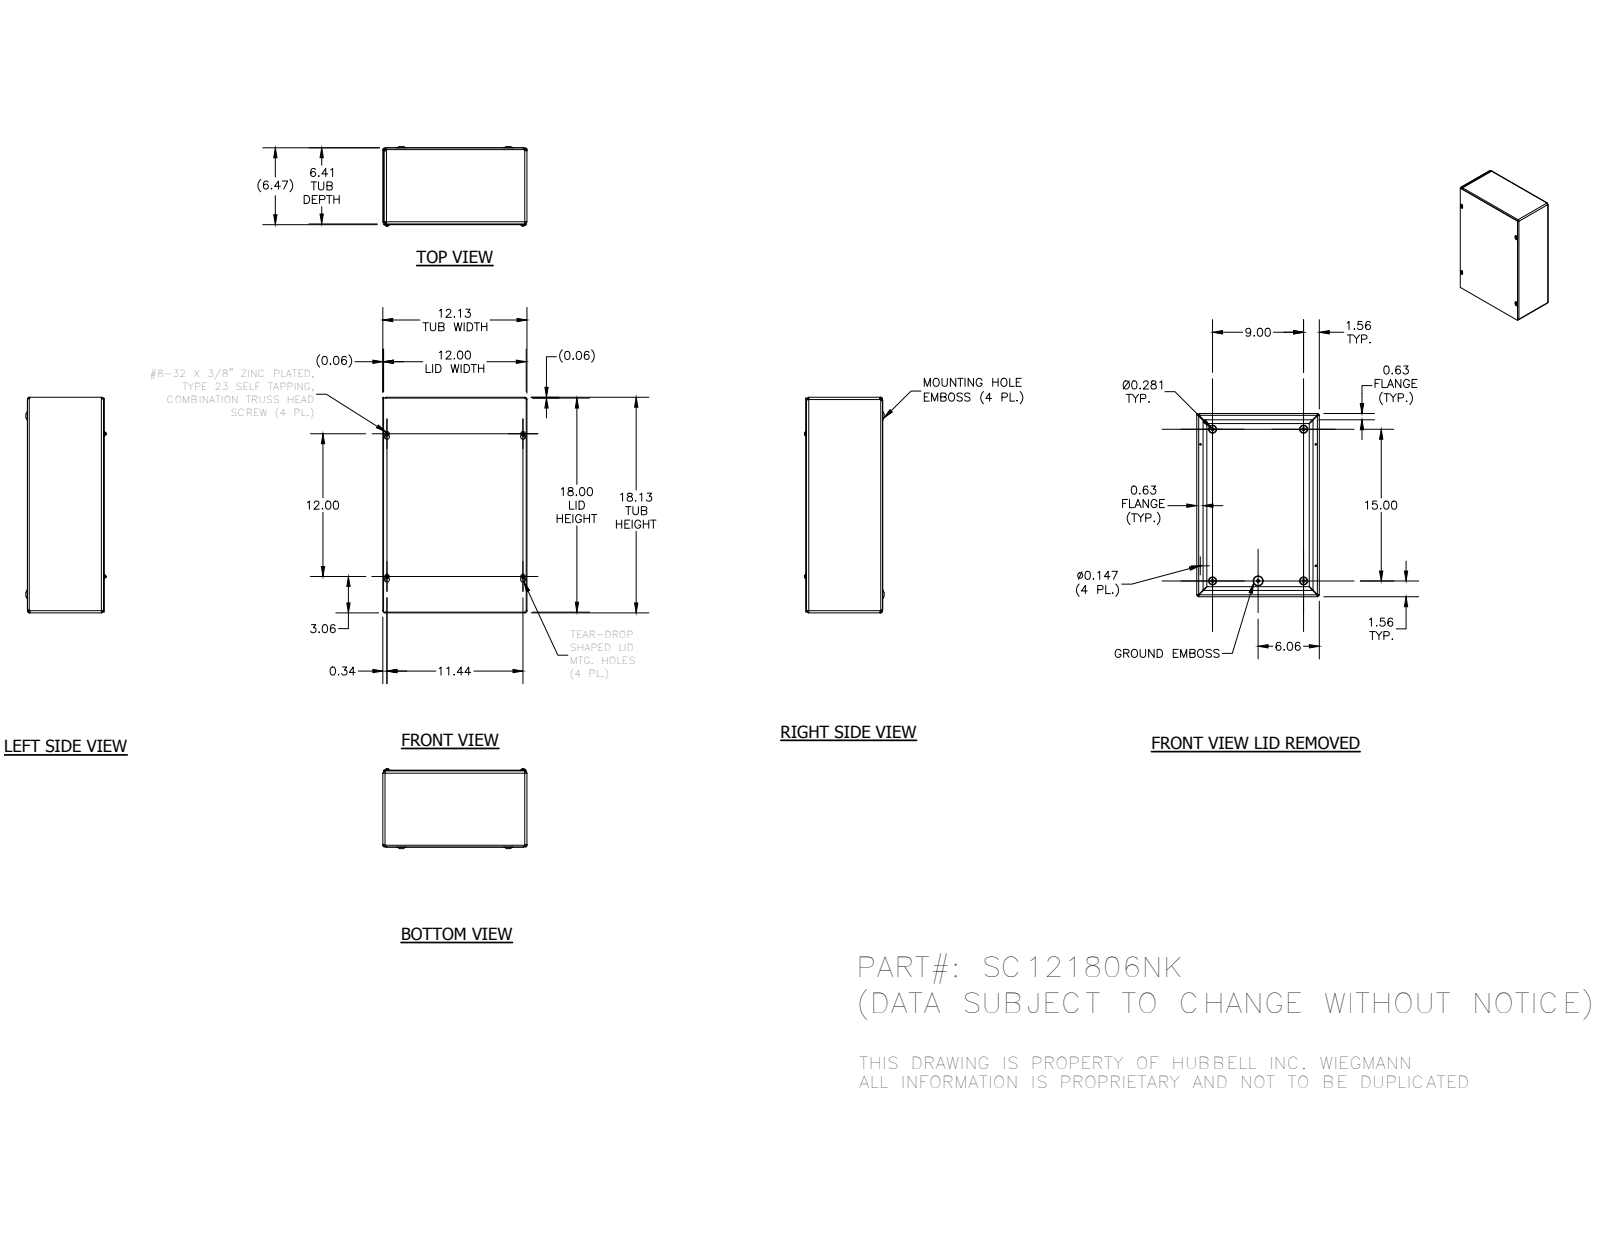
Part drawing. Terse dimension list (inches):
name: SC1218BKP; SC121806NKWRA; SC1218LID; 34056 (+1 more)
written by: Autodesk Inventor 2014 (AUTOMOTIVE_DESIGN)
unit: in
bodies: 7 solids, 357 faces (132 planar, 67 cylindrical, 158 other)
size: 18.125 × 12.125 × 6.693
volume: 55.1 in³; area: 1 792 in²
holes: 4× ⌀0.147, 4× ⌀0.3, 1× ⌀0.165
bosses: 4× ⌀0.384, 4× ⌀0.164, 1× ⌀0.228
rounds: 12× R0.125, 8× R0.187, 4× R0.055, 4× R0.062, 4× R0.094, 4× R0.117, 4× R0.124, 4× R0.156
face distances: 0.062, 6.343, 6.405, 0.063, 0.062, 6.406, 6.468, 12.063, 12.001, 12.125
hole spacings: 1.933, 13.555, 4.5, 9, 10.328, 10.328, 11.437, 12
